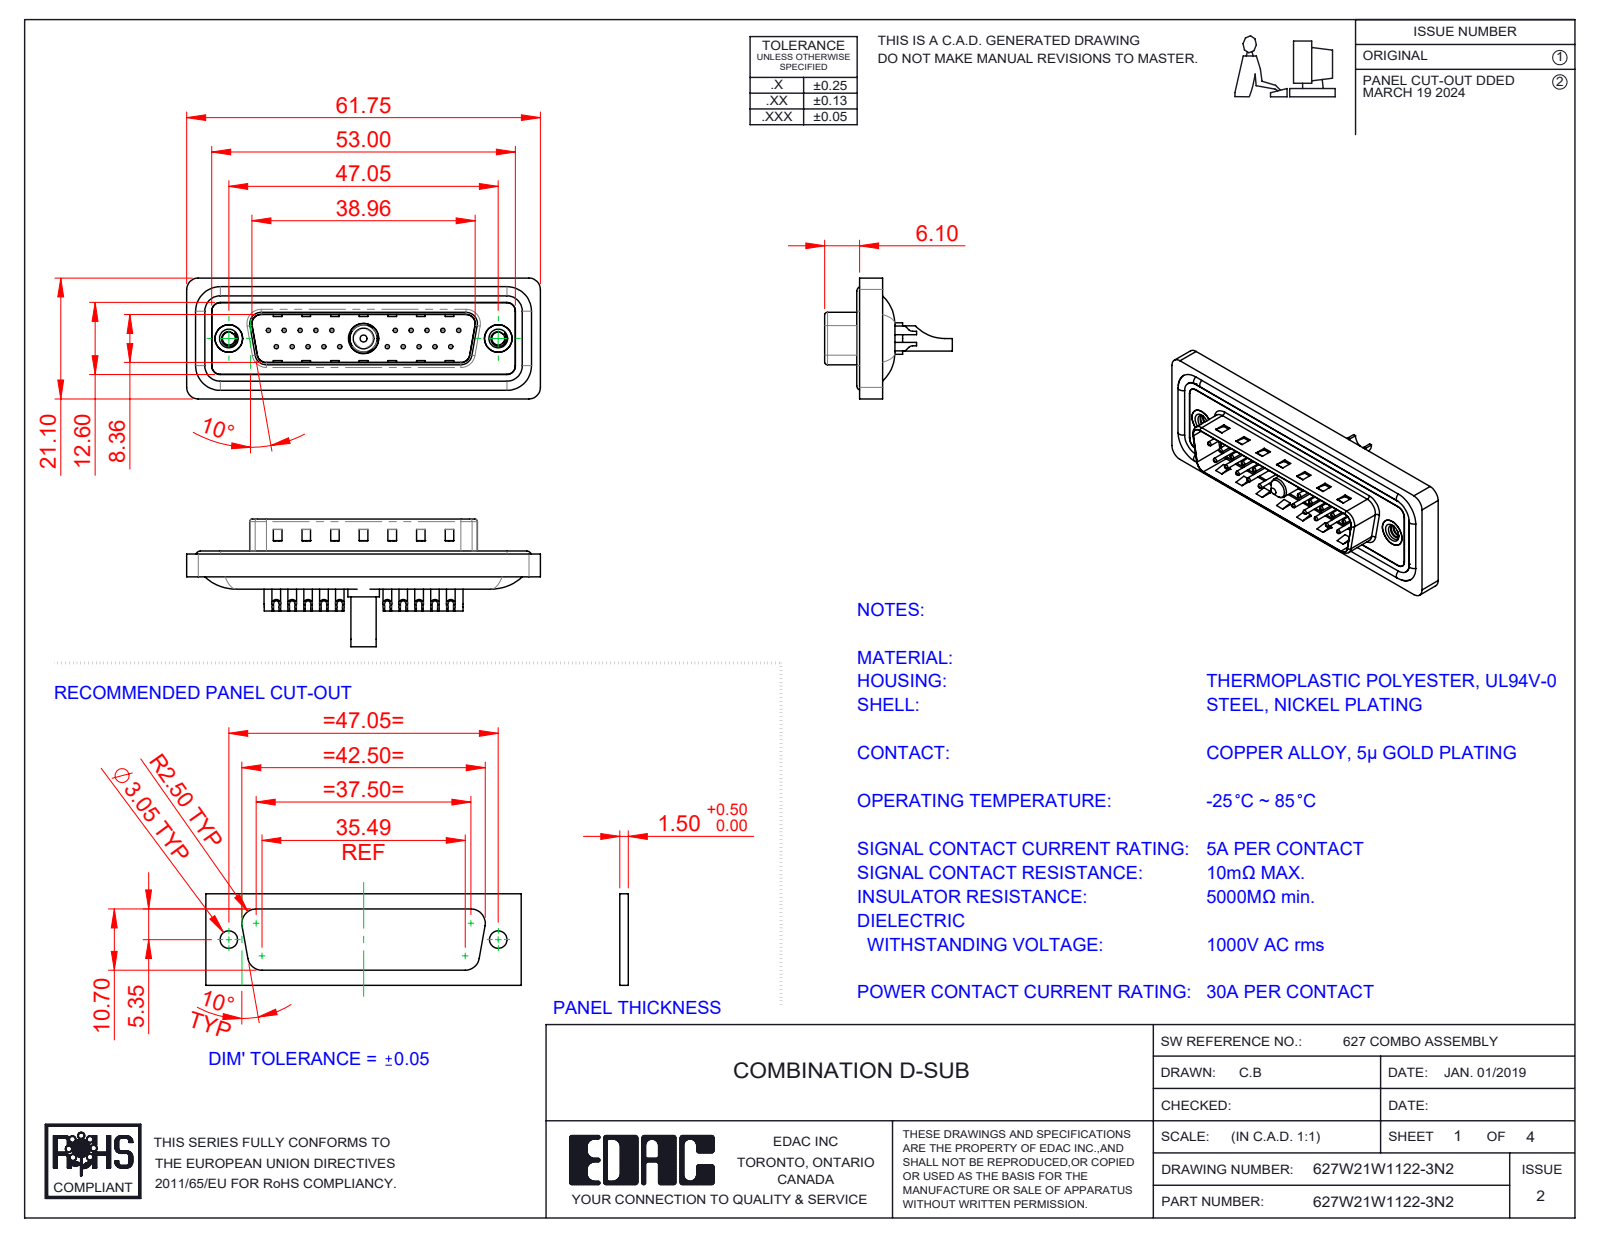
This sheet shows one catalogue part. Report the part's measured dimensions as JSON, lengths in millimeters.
{"part_name": "627Combo Contact Row 1_22; 627Combo Contact Row 2_22; 627W21W1122-3N2; 627Combo Shell Rear_25 Contacts (+5 more)", "step_written_by": "SolidWorks 2023 (CONFIG_CONTROL_DESIGN)", "units": "millimeters", "bodies": {"solids": 29, "faces": 1268, "planar": 402, "cylindrical": 530, "other": 336}, "overall_size": [61.75, 22.3, 21.1], "volume_mm3": 7252, "surface_area_mm2": 12220, "round_holes": [[0.75, 20], [1, 20], [1.6, 20], [2, 20], [2.26, 2], [4, 2], [4.8, 2], [5, 2], [3.5, 1], [4.85, 1], [5.3, 1]], "round_bosses_or_shafts": [[1.5, 20], [1.6, 4], [4.9, 2], [5.5, 1], [5.2, 1], [4.75, 1], [4.4, 1], [3.75, 1]], "partial_cylinders_radius": [[1.5, 22], [2, 18], [0.5, 8], [1.6, 8], [1, 6], [0.25, 4], [0.6, 4], [0.65, 4]], "face_to_face_distances": [0.4, 1.5, 1.1, 1.6, 0.5, 3.1, 2.9, 4.1, 0.82, 9.58], "hole_center_spacings": [3.16, 2.77, 5.54, 8.31, 5.04, 19.39, 20.97, 22.16]}
